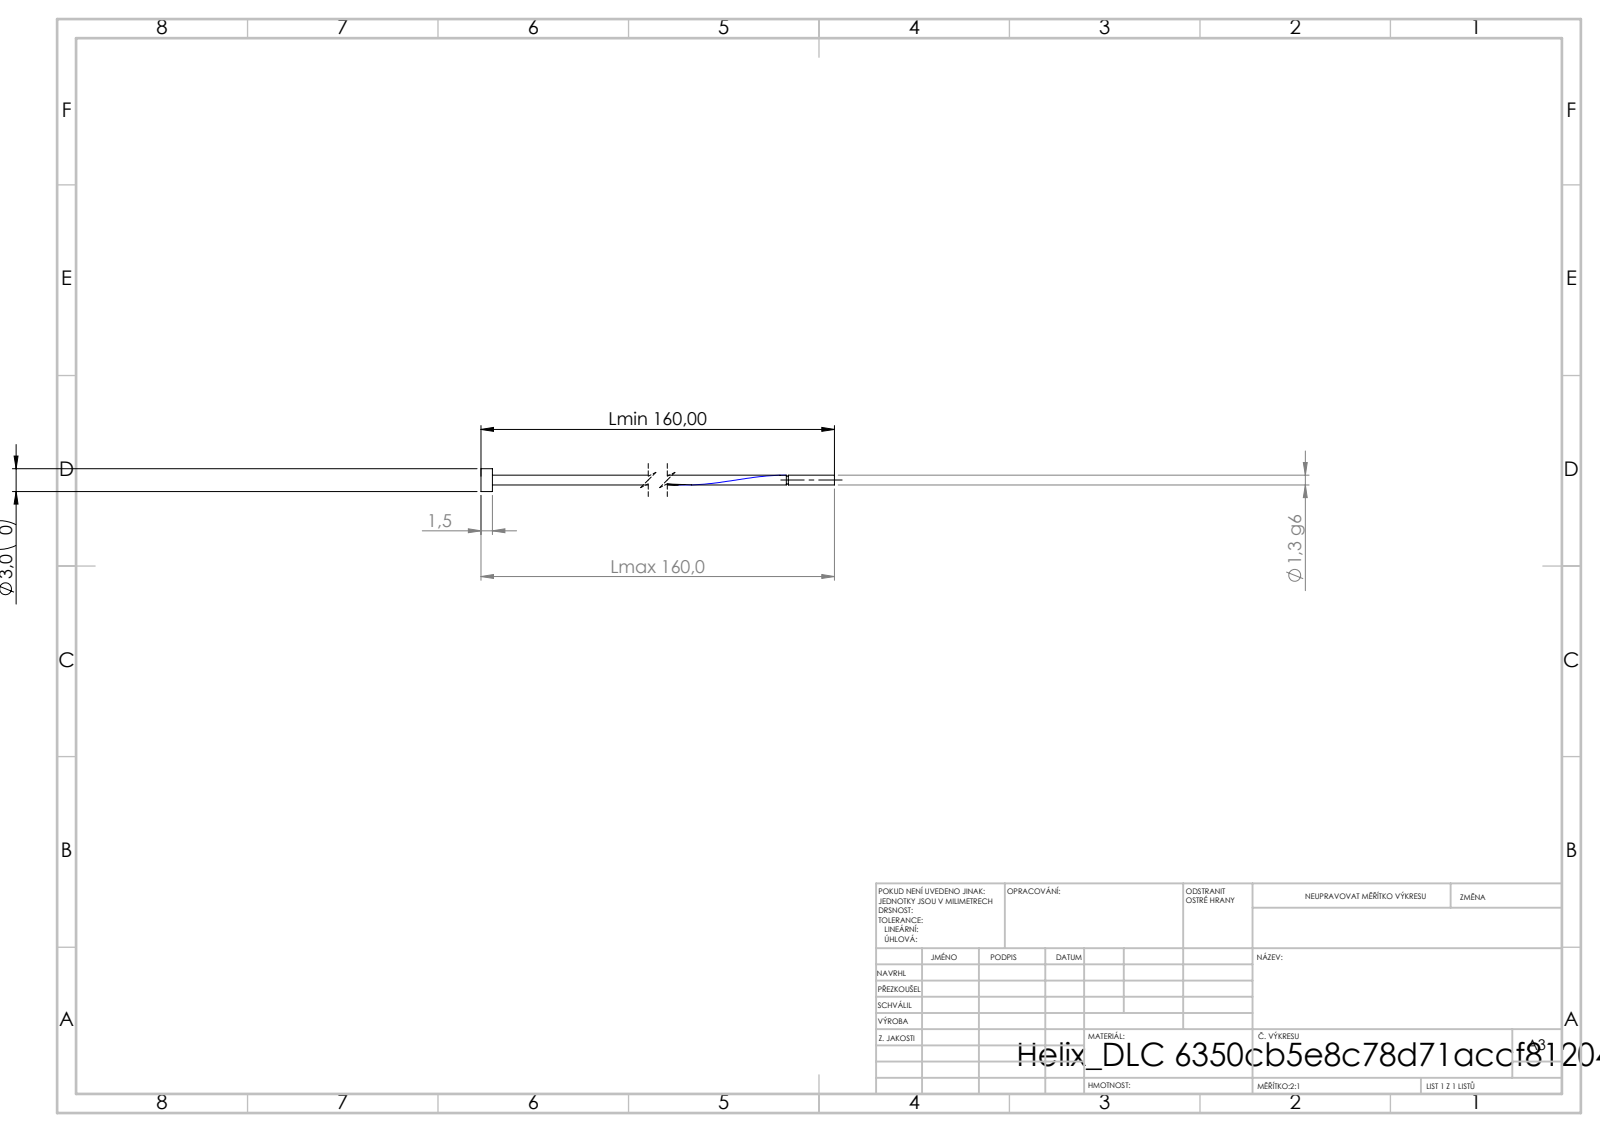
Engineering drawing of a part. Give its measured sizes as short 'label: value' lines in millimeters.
written by: SolidWorks 2019 (CONFIG_CONTROL_DESIGN)
unit: mm
bodies: 1 solid, 16 faces (6 planar, 9 cylindrical, 1 other)
size: 160 × 3 × 3
volume: 266 mm³; area: 904 mm²
bosses: 1× ⌀3, 1× ⌀1.3, 1× ⌀1.04
face distances: 1.5, 160, 158.5, 153.95, 152.45, 6.05, 153.69, 152.19, 6.31, 73.69
